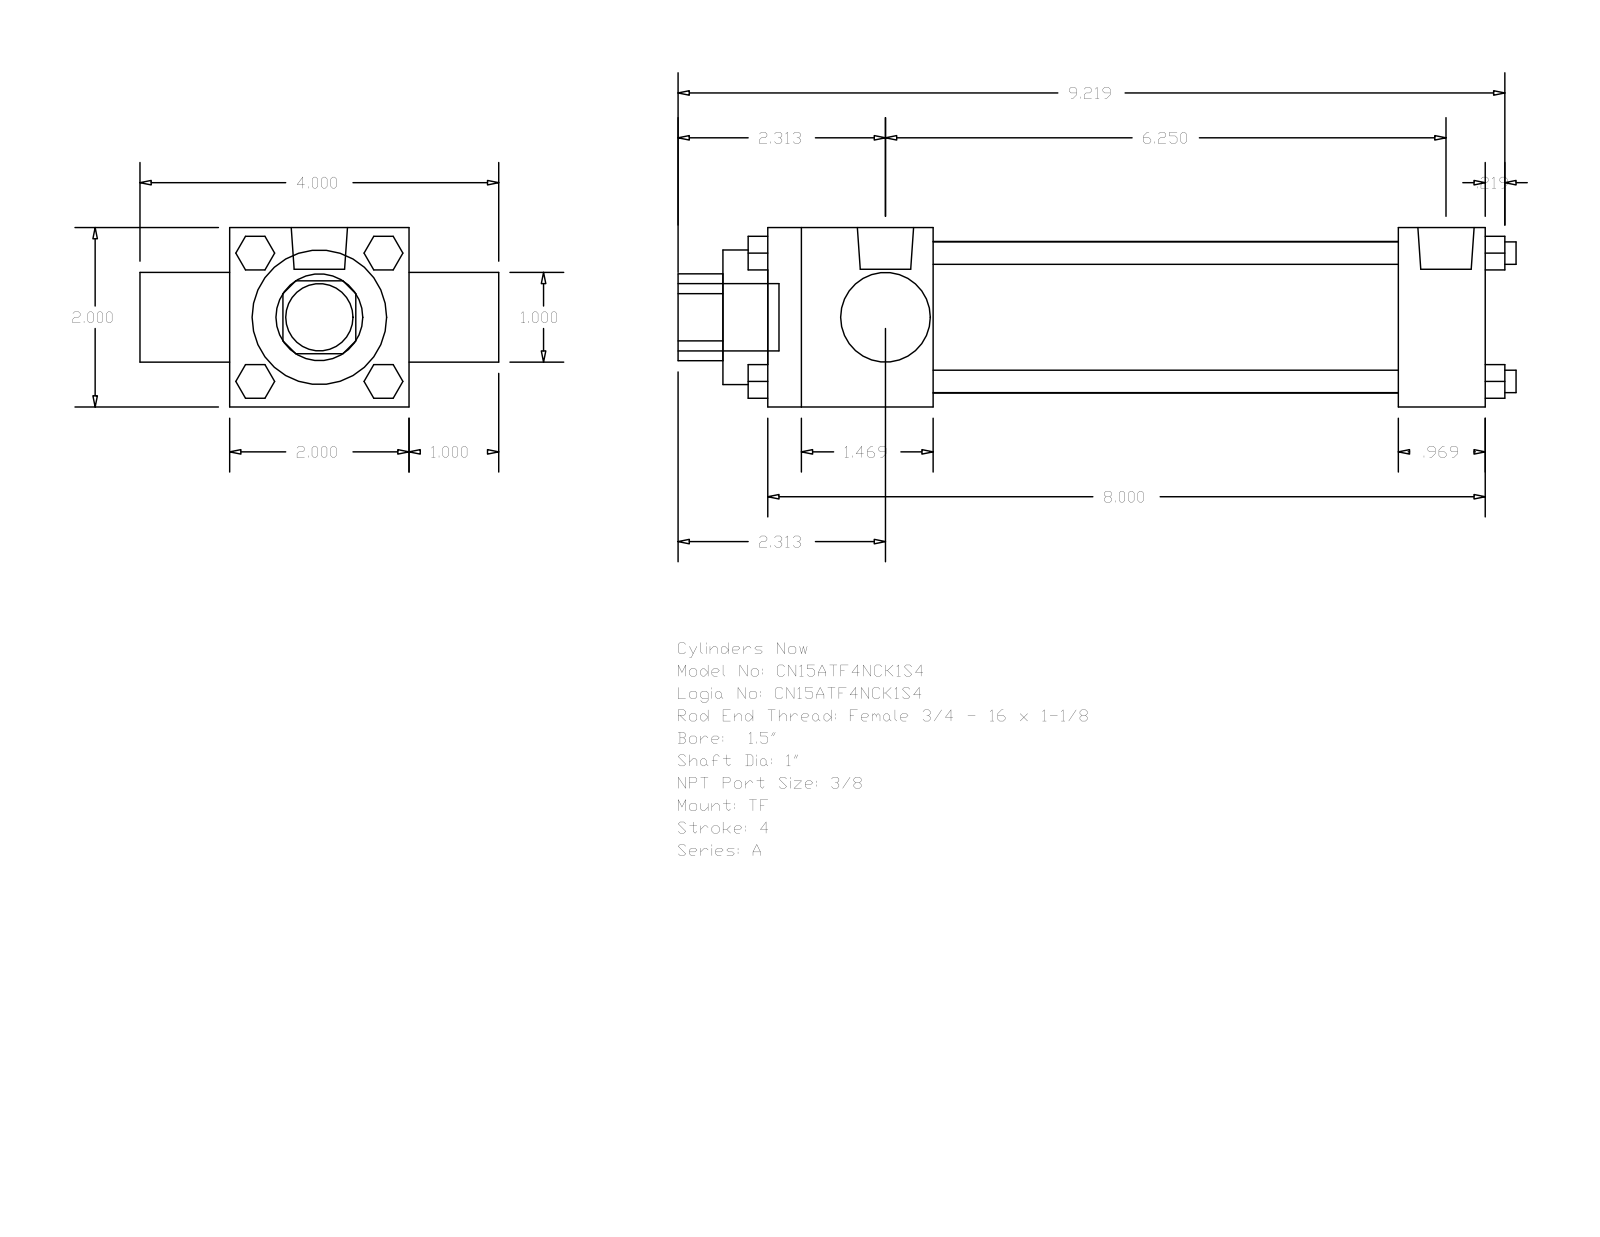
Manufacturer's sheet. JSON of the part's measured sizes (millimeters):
{"part_name": "A_TF__0150_1", "step_written_by": "GSSL Pune (CONFIG_CONTROL_DESIGN)", "units": "millimeters", "bodies": {"solids": 0, "faces": 120, "planar": 92, "cylindrical": 28, "other": 0}, "overall_size": [237.33, 101.6, 50.8], "round_holes": [[25.4, 2], [38.1, 1], [42.93, 1]], "round_bosses_or_shafts": [[6.35, 4], [5.56, 3], [15.93, 2], [19.05, 1]], "partial_cylinders_radius": [[12.29, 1]], "face_to_face_distances": [50.8, 25.4, 203.2, 76.2, 46.83, 178.59, 131.76, 156.37, 24.61, 12.7]}
